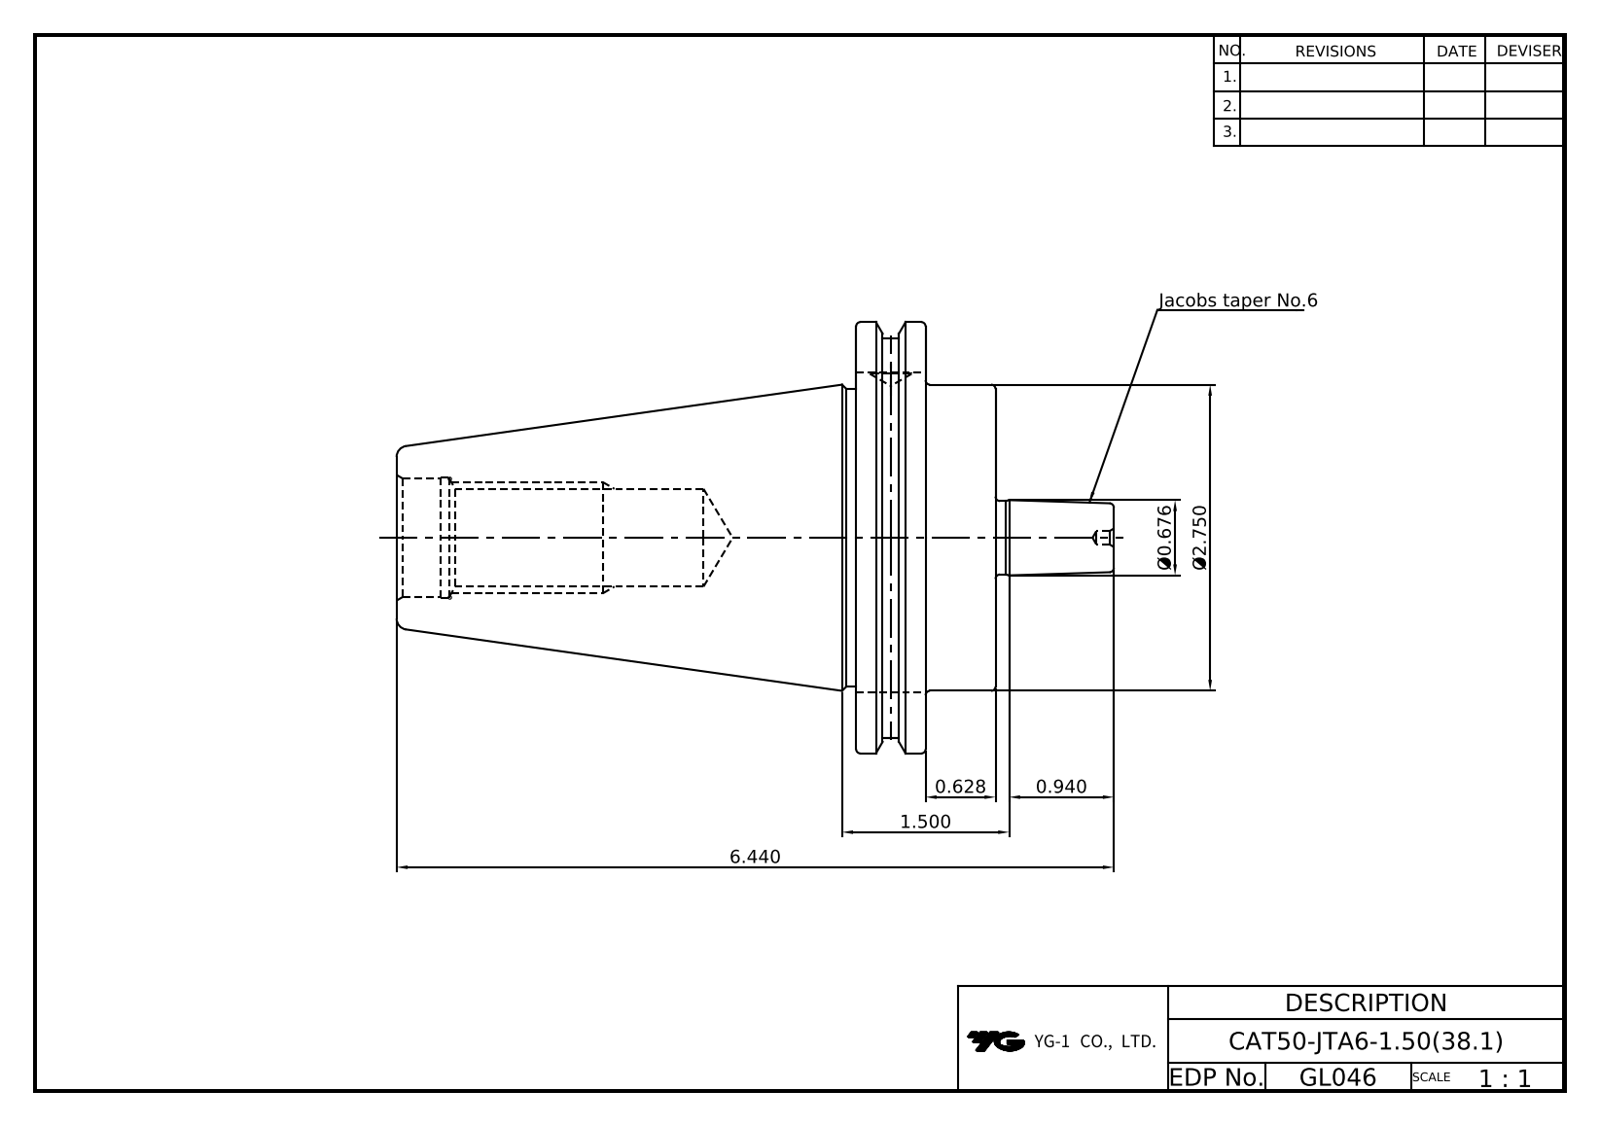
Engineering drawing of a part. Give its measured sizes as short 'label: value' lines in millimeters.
name: CAT50-JTA6-1.50(20231109)
written by: Autodesk Inventor 2024 (AUTOMOTIVE_DESIGN)
unit: mm
bodies: 1 solid, 60 faces (28 planar, 12 cylindrical, 20 other)
size: 163.58 × 98.42 × 94.69
volume: 404 042 mm³; area: 45 834 mm²
holes: 1× ⌀9.53, 1× ⌀21.97, 1× ⌀26.2
bosses: 1× ⌀98.42, 1× ⌀91.29, 1× ⌀69.85, 1× ⌀69.25, 1× ⌀16.77
face distances: 15.95, 15.88, 31.83, 104.77, 120.65, 136.6, 73.03, 25.9, 114.64, 9.87
